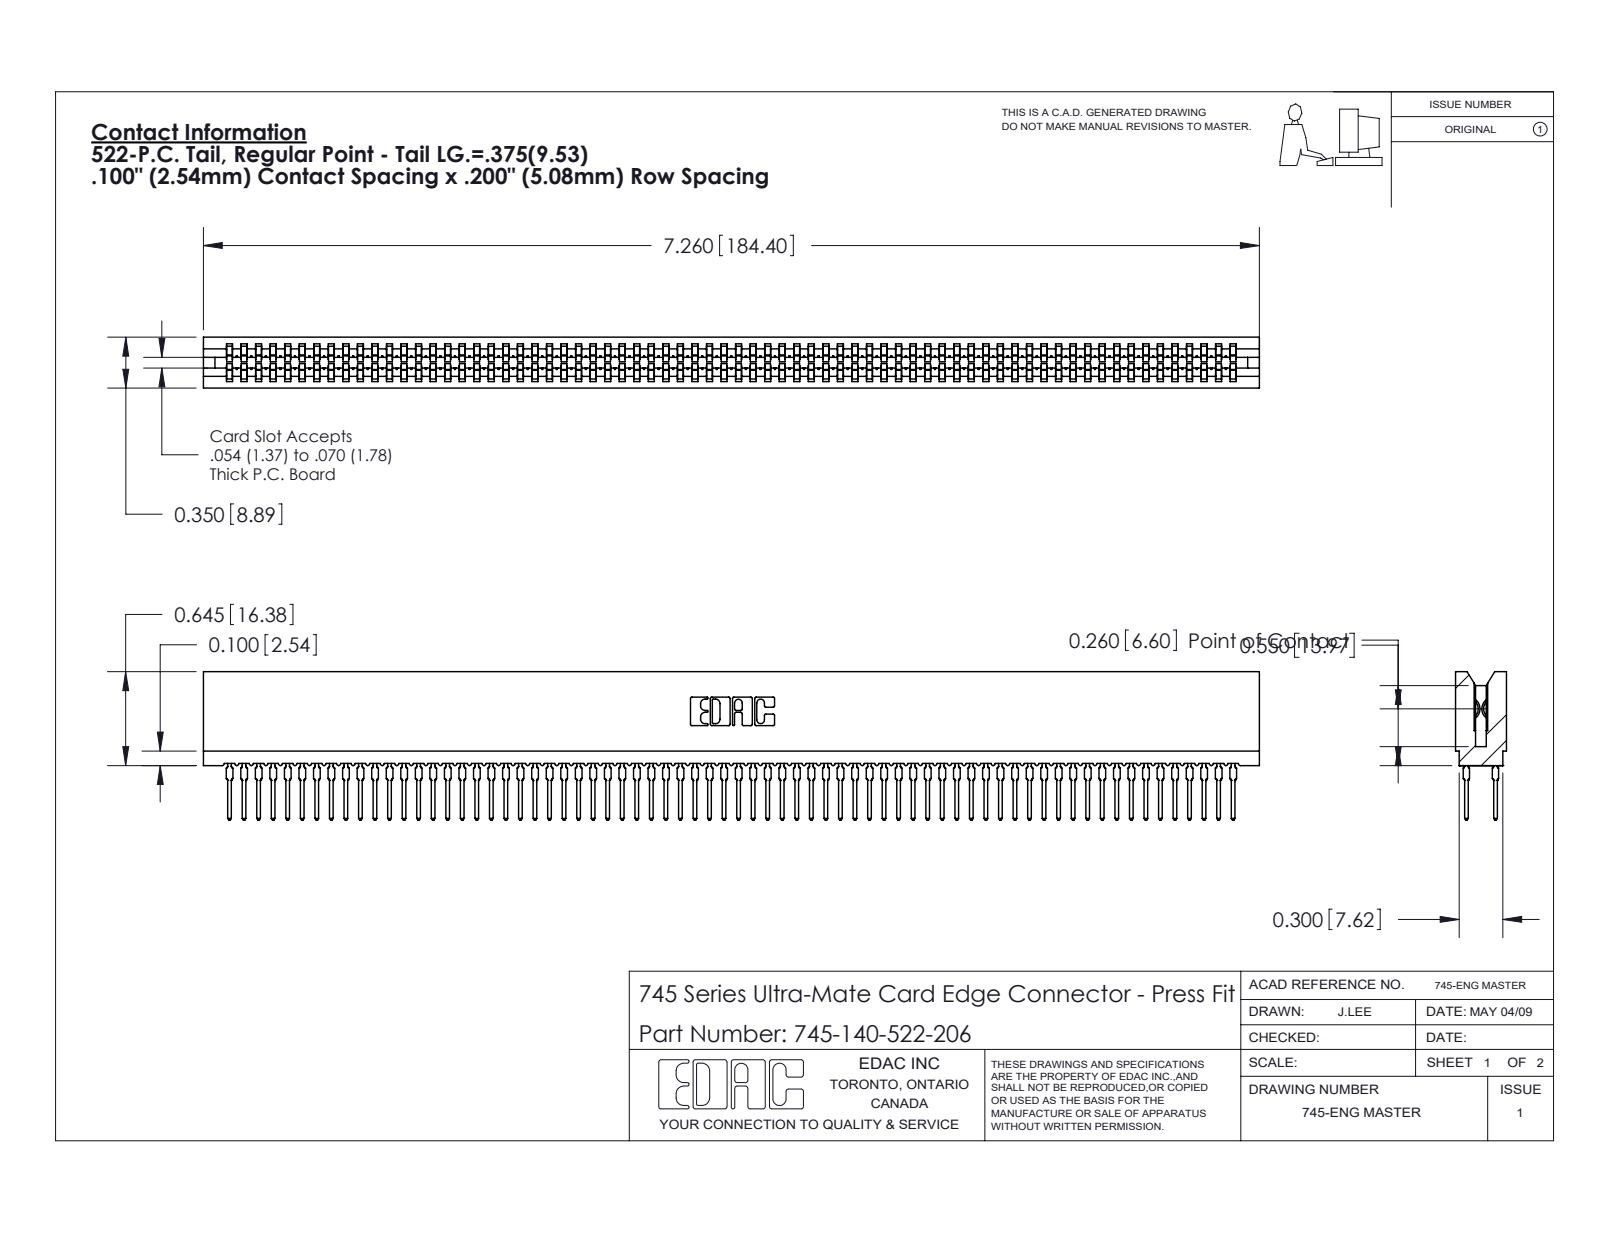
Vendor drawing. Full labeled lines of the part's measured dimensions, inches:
Part name (STEP PRODUCT): 745 Part_Insulator Option - 06; 745-140-522-206; 745-292-001_522
STEP written by: SolidWorks 2020 (CONFIG_CONTROL_DESIGN)
Units: inches
Bodies: 141 solids, 12626 faces (6496 planar, 2490 cylindrical, 3640 other)
Overall size (bounding box): 7.26 × 1.021 × 0.35
Volume: 1.011 in³ · Surface area: 53.99 in²
Partial cylindrical surfaces — rounded edges, fillets, slot ends (radius × count): R0.021 ×280, R0.015 ×140, R0.01 ×22, R0.005 ×8, R0.011 ×8, R0.007 ×6, R0.031 ×6, R0.026 ×3
Main face-to-face distances: 0.35, 0.063, 0.287, 0.045, 0.305, 0.018, 0.243, 0.138, 0.212, 0.093
